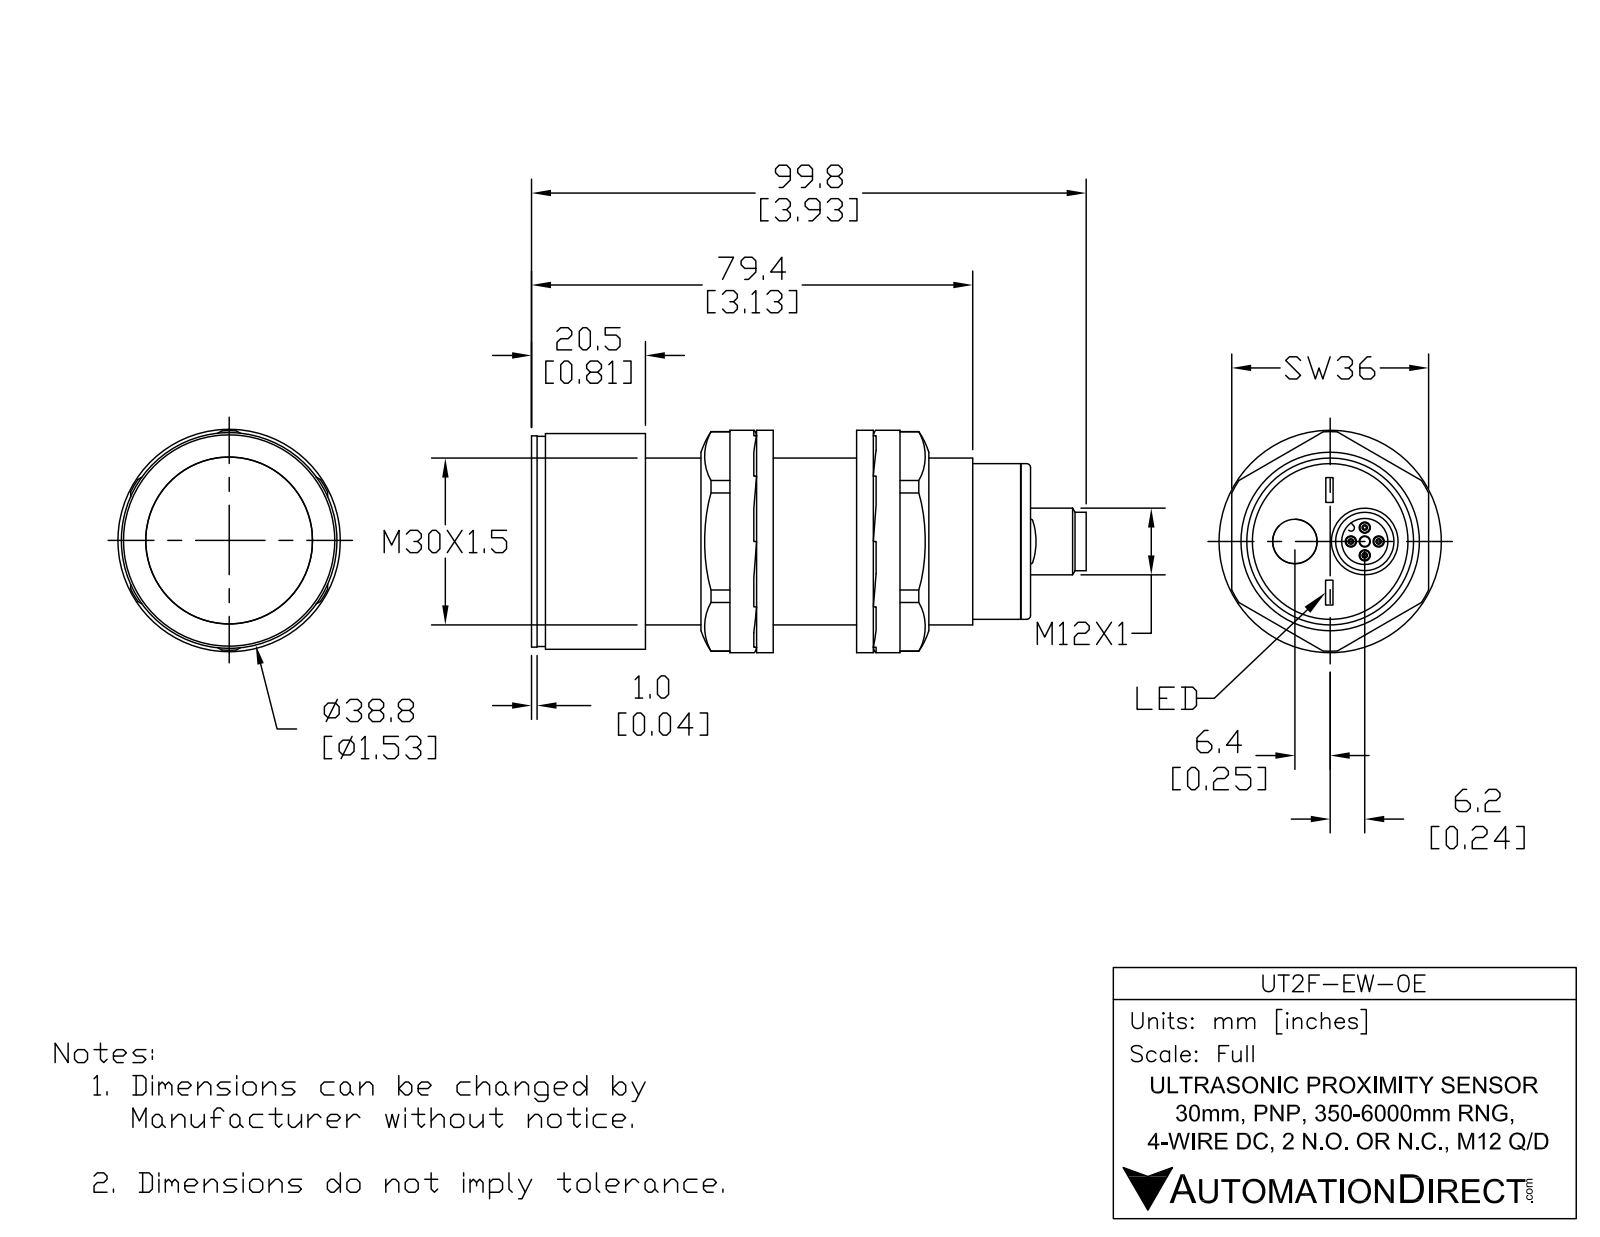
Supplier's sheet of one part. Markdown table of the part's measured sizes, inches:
| quantity | value |
| --- | --- |
| part name | UT2F-EW-0E |
| STEP written by | SolidWorks 2017 (AUTOMOTIVE_DESIGN) |
| units | inches |
| bodies | 5 solids, 108 faces (31 planar, 47 cylindrical, 30 other) |
| overall size | 3.894 × 1.528 × 1.528 |
| volume | 4.372 in³ |
| surface area | 24.88 in² |
| round holes (diameter × count) | 0.071 × 4, 0.315 × 1, 0.327 × 1, 0.372 × 1, 1.299 × 1 |
| round bosses / shafts (diameter × count) | 0.039 × 4, 1.528 × 1, 1.488 × 1, 1.181 × 1, 1.102 × 1, 0.472 × 1, 0.413 × 1, 0.364 × 1 |
| partial cylindrical surfaces (radius × count) | 0.012 × 2, 0.024 × 1 |
| main face-to-face distances | 3.37, 0.059, 3.429, 0.767, 0.709, 2.661, 0.059, 3.429, 0.071, 3.5 |
| hole center spacings | 0.098, 0.139, 0.197, 0.264, 0.505, 0.146, 0.245, 0.25 |
